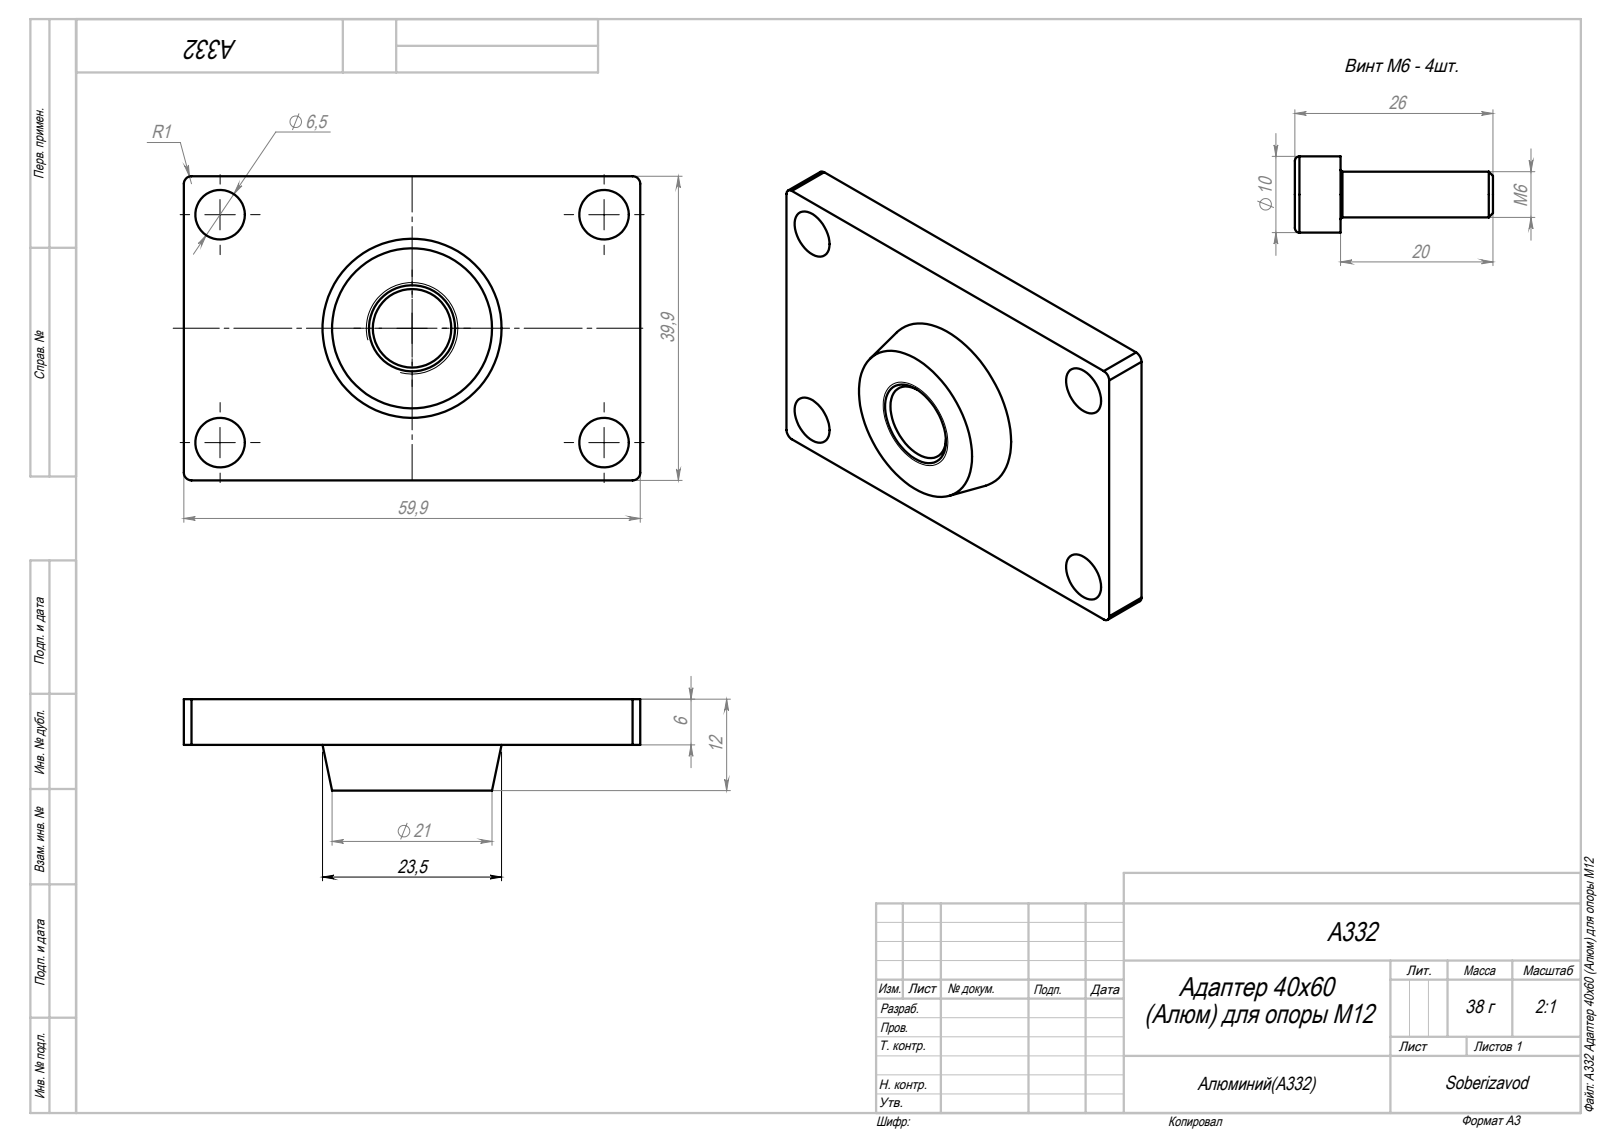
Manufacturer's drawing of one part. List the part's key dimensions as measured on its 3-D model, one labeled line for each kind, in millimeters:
Part name (STEP PRODUCT): A332 Адаптер 40х60 (Алюм) для опоры М12; A332 Адаптер 40х60 (Алюм) для опоры М12, Винт(1)_00; A332 Адаптер 40х60 (Алюм) для опоры М12_00
STEP written by: SolidWorks 2018 (AUTOMOTIVE_DESIGN)
Units: millimetres
Bodies: 5 solids, 137 faces (57 planar, 50 cylindrical, 30 other)
Overall size (bounding box): 60.4 × 39.95 × 26
Volume: 18 577 mm³ · Surface area: 9 731 mm²
Round holes (diameter × count): ⌀5.7 ×6, ⌀1 ×4, ⌀6.5 ×4, ⌀10.3 ×1
Round bosses / shafts (diameter × count): ⌀10 ×4, ⌀6 ×4
Partial cylindrical surfaces — rounded edges, fillets, slot ends (radius × count): R1 ×4
Main face-to-face distances: 6, 12, 39.9, 59.9, 3, 0.46, 5.54, 11.54, 9, 8.54
Hole centre spacings: 9.1, 12.1, 14.45, 19.84, 19.92, 25.93, 29.28, 29.33
